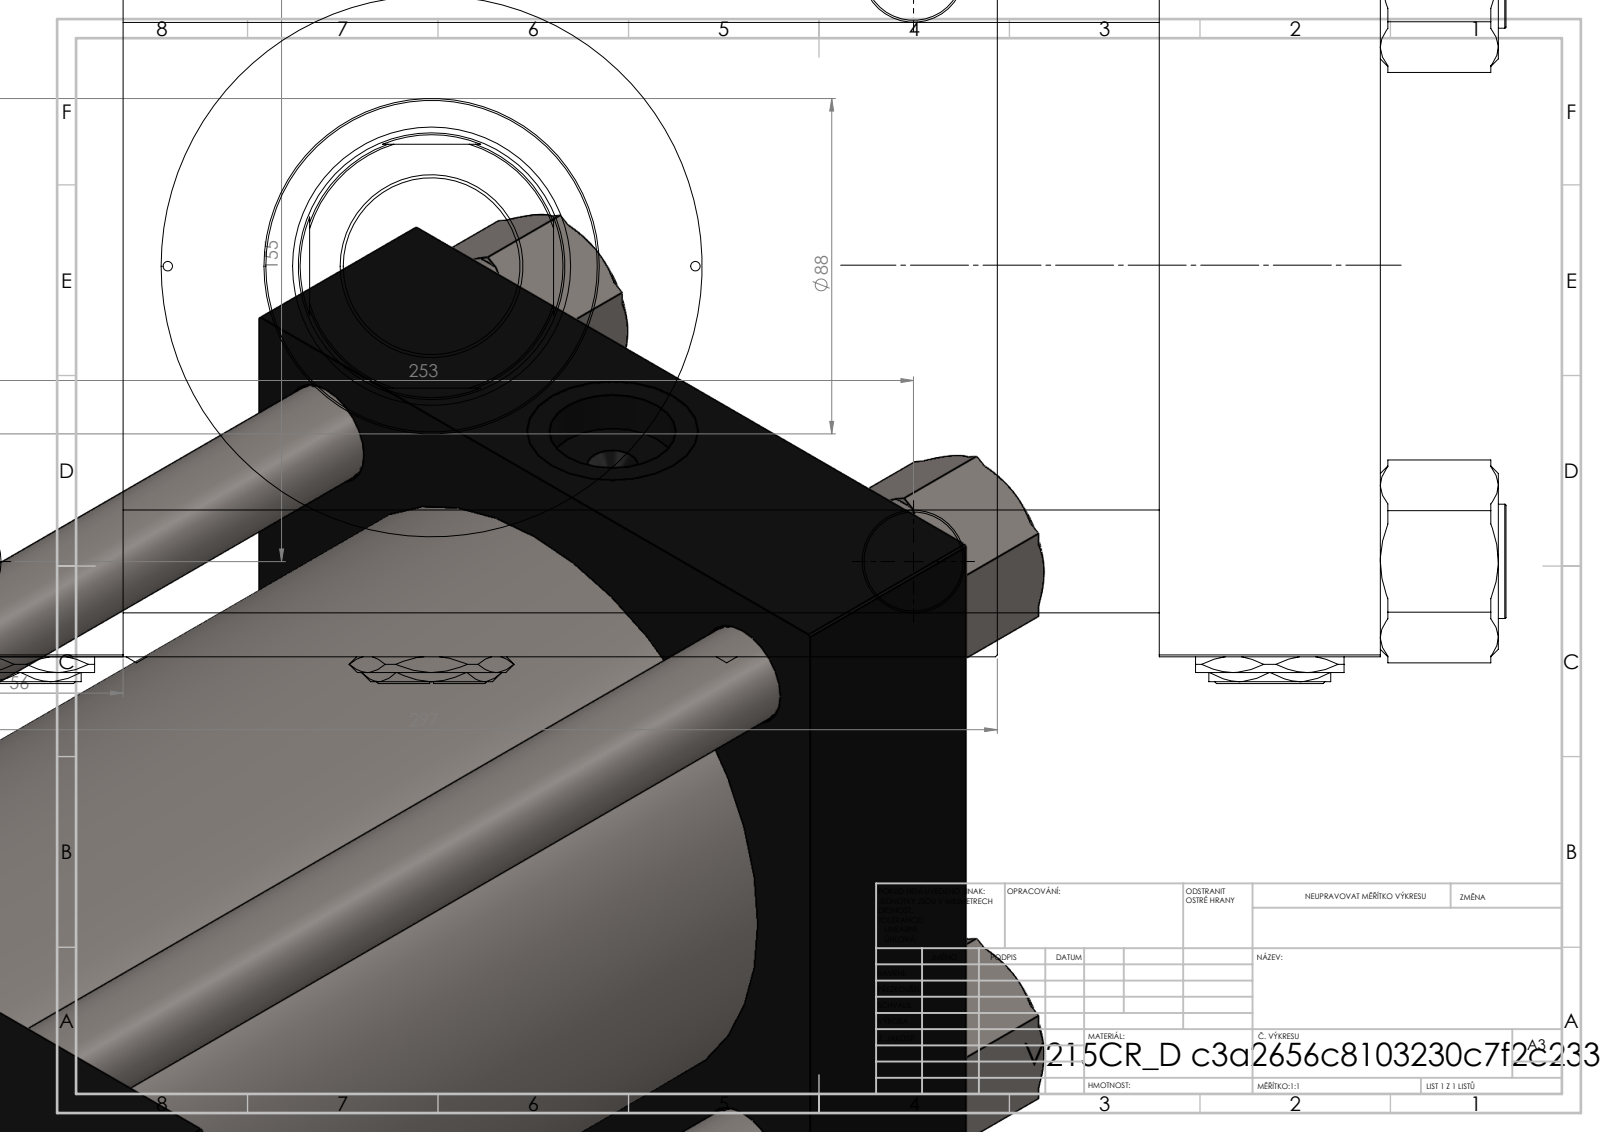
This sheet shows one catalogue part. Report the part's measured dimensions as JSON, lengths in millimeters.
{"part_name": "V215_VC_A; Zatka_pro_OIL_PORT; NUT_M5_D; V215CR_D_Body (+3 more)", "step_written_by": "SolidWorks 2019 (CONFIG_CONTROL_DESIGN)", "units": "millimeters", "bodies": {"solids": 14, "faces": 1270, "planar": 598, "cylindrical": 106, "other": 566}, "overall_size": [539, 297, 213.57], "volume_mm3": 9358000, "surface_area_mm2": 1035000, "round_holes": [[26, 4], [27, 4], [2.5, 2], [7, 2], [33.24, 2], [45, 2], [46.5, 1], [70, 1], [73, 1], [120, 1], [142, 1], [160, 1]], "round_bosses_or_shafts": [[30, 4], [166, 1], [88, 1], [48, 1], [46, 1]], "partial_cylinders_radius": [[34, 1]], "face_to_face_distances": [58, 330, 272, 386, 328, 56, 205, 46, 251, 72], "hole_center_spacings": [49.05, 77.88, 96.35, 109.53, 148.35, 154.9, 162.53, 165.89]}
